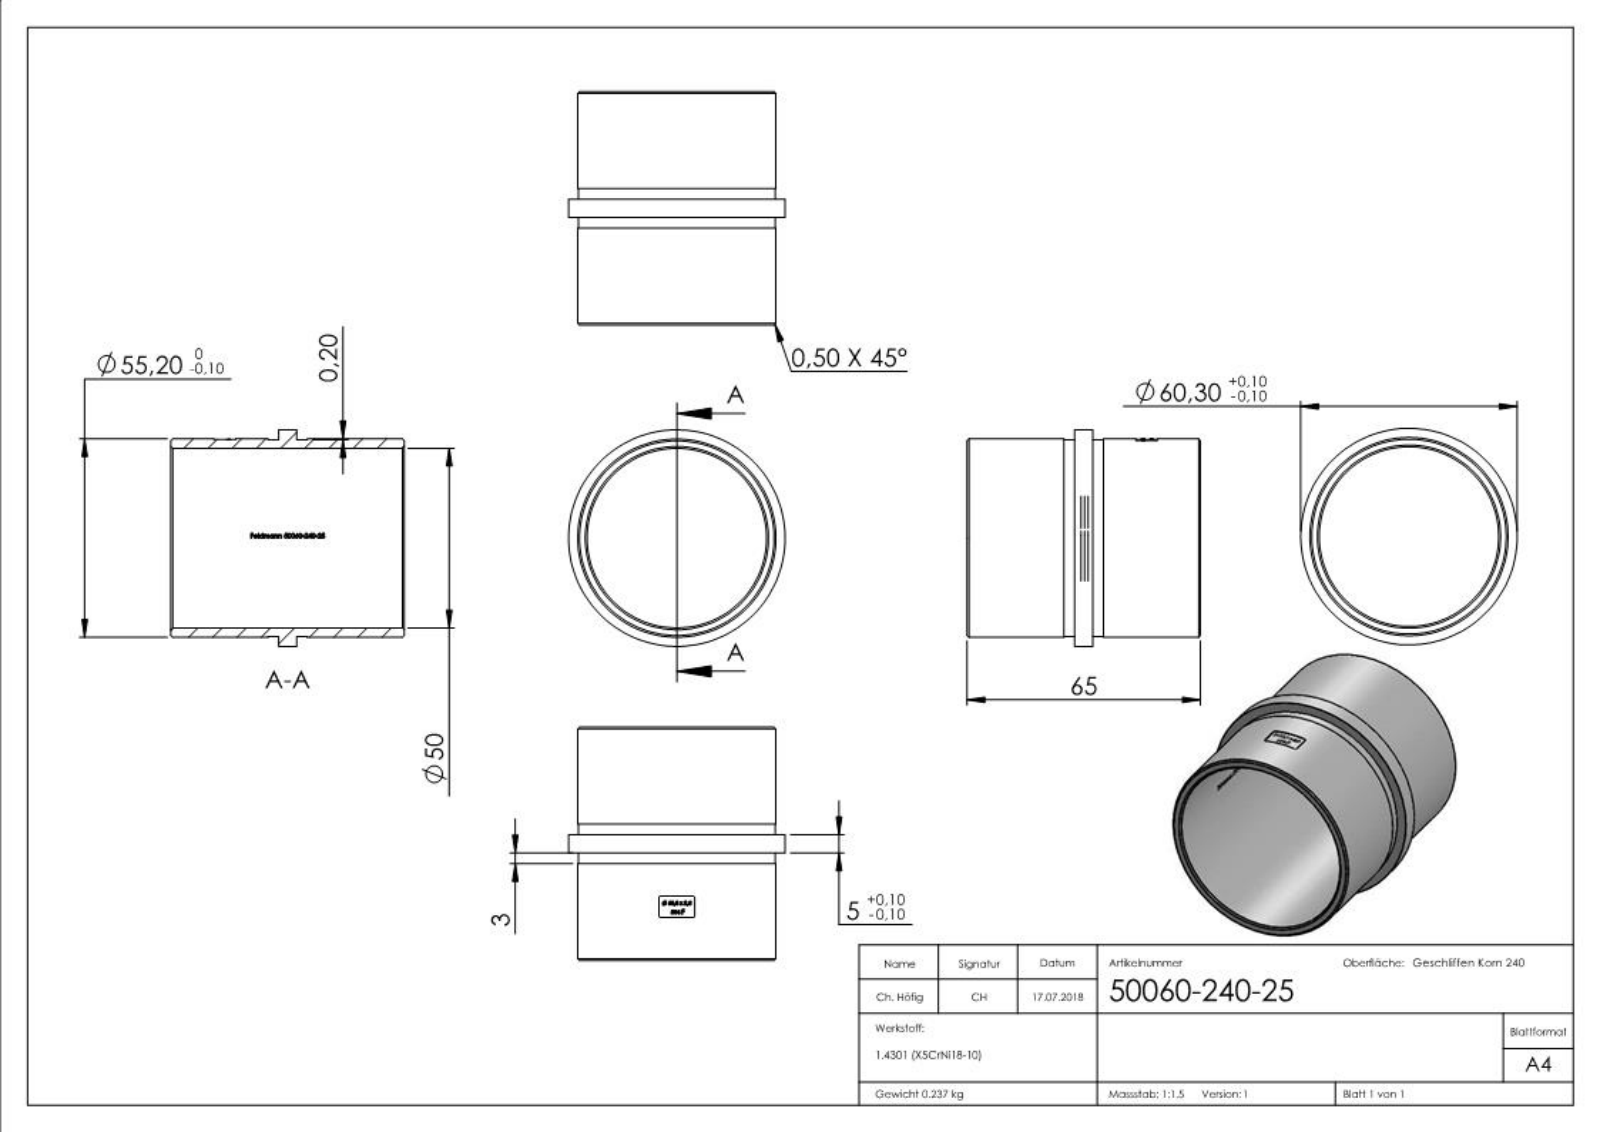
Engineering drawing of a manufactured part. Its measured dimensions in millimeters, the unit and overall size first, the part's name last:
Units: millimetres
Overall size (bounding box): 65 × 60.3 × 60.3
Round holes (diameter × count): ⌀50 ×1
Round bosses / shafts (diameter × count): ⌀60.3 ×1, ⌀55.2 ×1, ⌀54.8 ×1
Partial cylindrical surfaces — rounded edges, fillets, slot ends (radius × count): R0.5 ×4, R25.1 ×1, R27.5 ×1
Main face-to-face distances: 30, 35, 5, 65, 27, 38, 3, 8, 11, 12
Volume: 29 943 mm³ · Surface area: 23 304 mm²
Bodies: 1 solid, 469 faces (187 planar, 71 cylindrical, 211 other)
Part name (STEP PRODUCT): 50060-240-25
STEP written by: SolidWorks 2015 (CONFIG_CONTROL_DESIGN)
